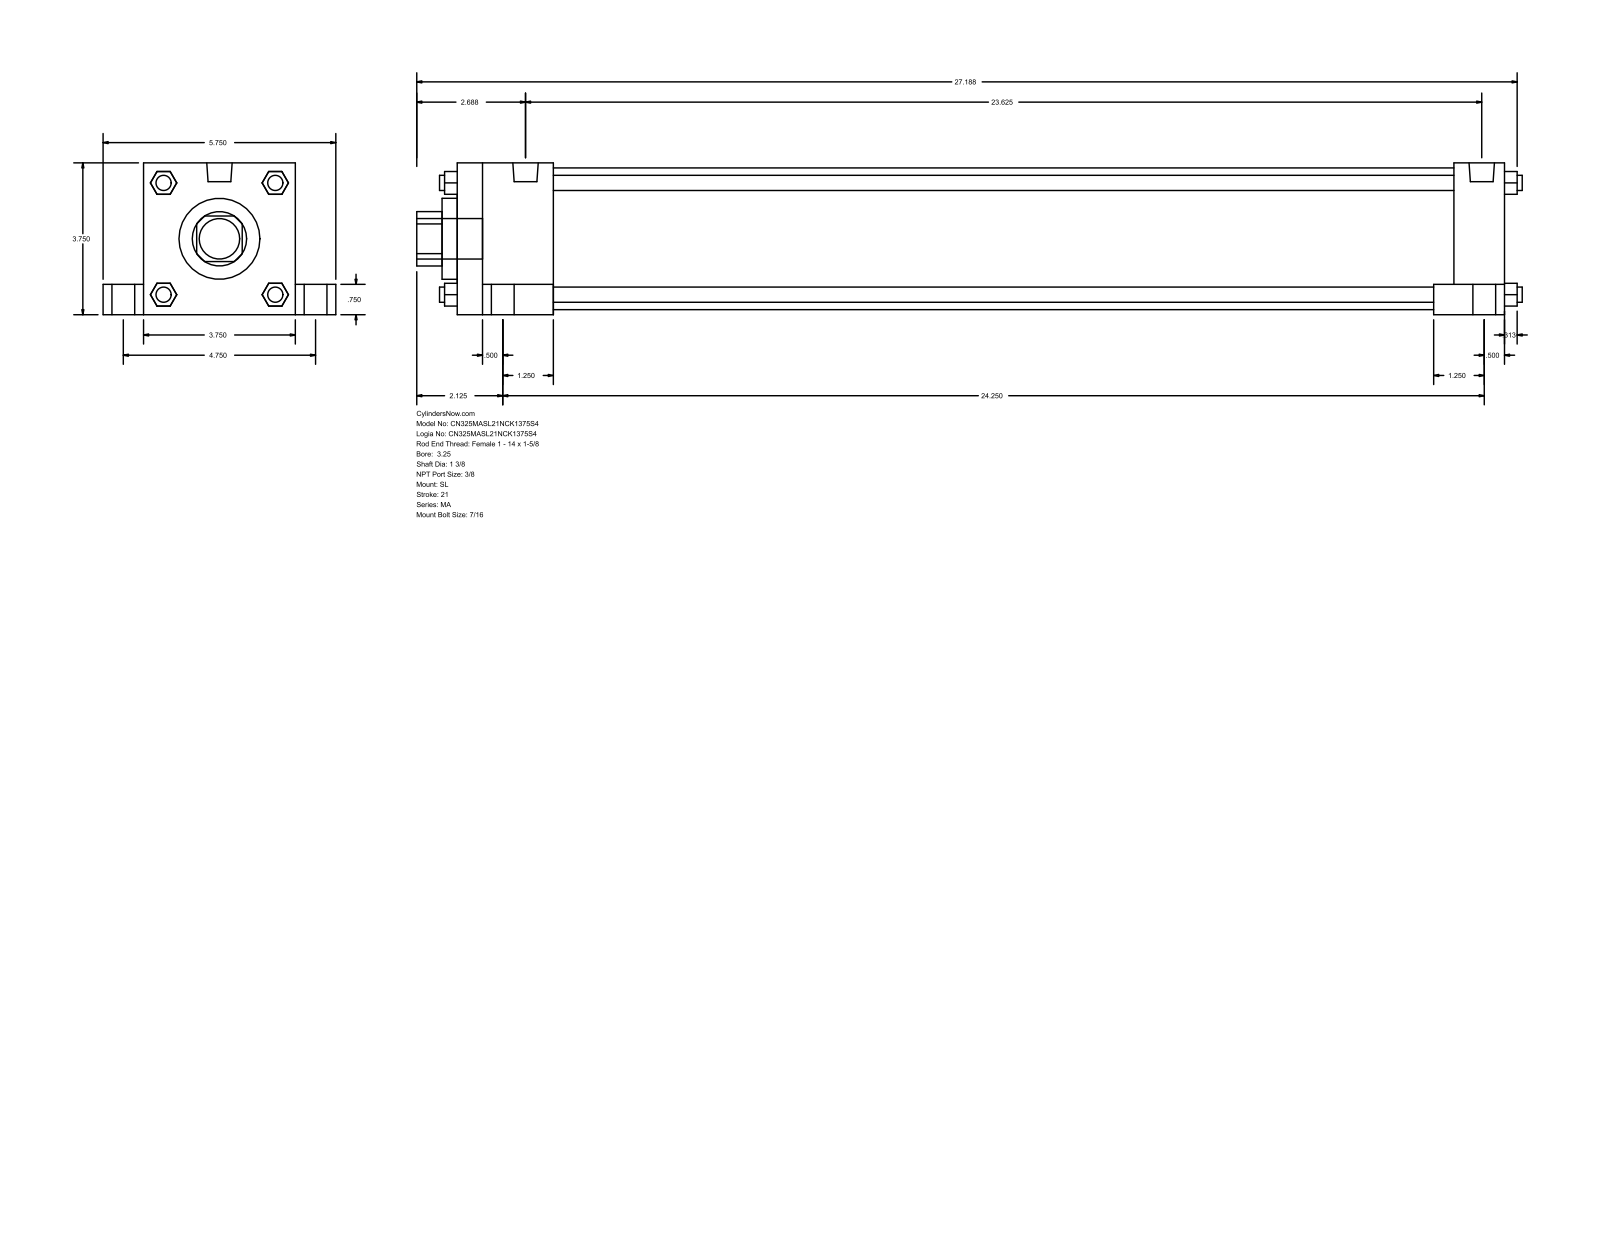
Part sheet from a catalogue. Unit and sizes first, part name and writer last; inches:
Units: inches
Overall size (bounding box): 27.313 × 5.75 × 3.75
Round holes (diameter × count): ⌀1.375 ×1, ⌀2 ×1, ⌀3.5 ×1
Round bosses / shafts (diameter × count): ⌀0.813 ×4, ⌀0.563 ×4, ⌀0.437 ×4, ⌀0.375 ×4, ⌀0.627 ×2, ⌀1 ×1
Partial cylindrical surfaces — rounded edges, fillets, slot ends (radius × count): R0.672 ×1
Main face-to-face distances: 3.75, 25.875, 1, 4.75, 24.625, 1.25, 2.375, 22.25, 23.5, 0.75
Bodies: 0 solids, 148 faces (112 planar, 36 cylindrical, 0 other)
Part name (STEP PRODUCT): MA_SL__0325_1.375
STEP written by: GSSL Pune (CONFIG_CONTROL_DESIGN)
